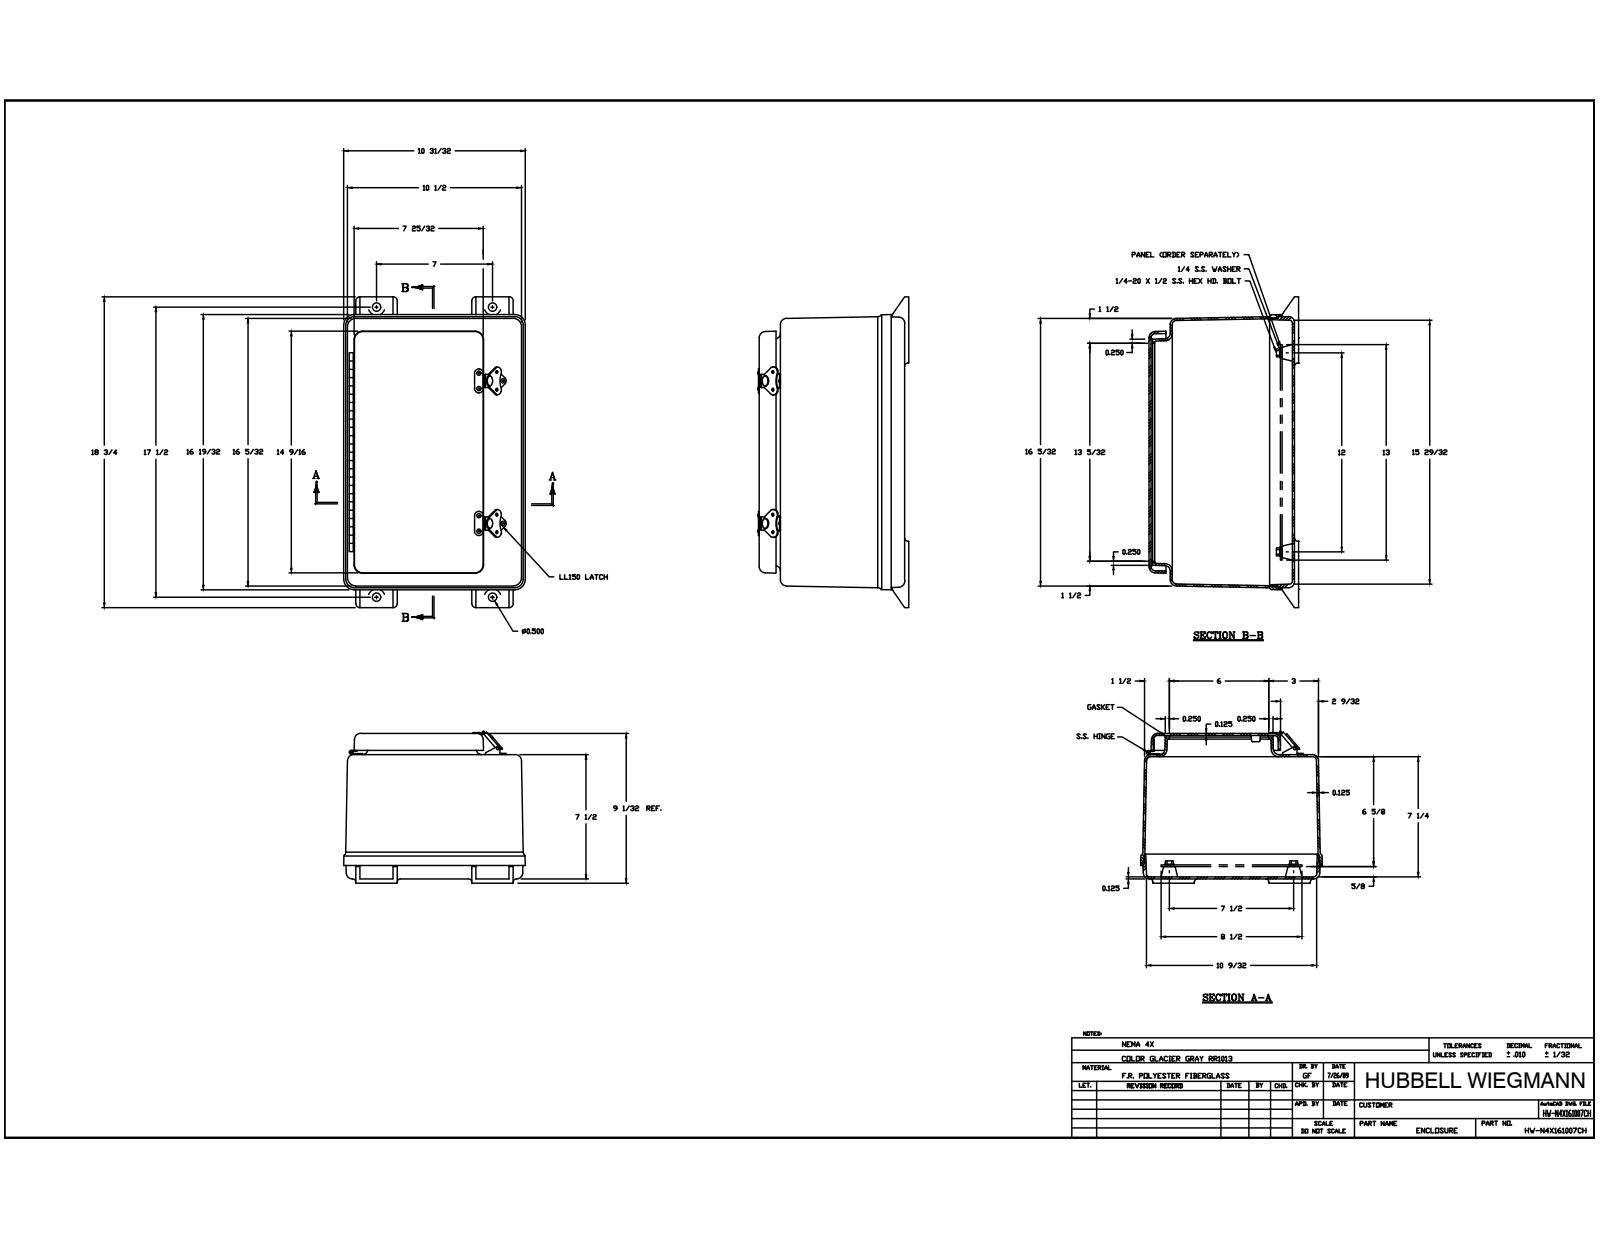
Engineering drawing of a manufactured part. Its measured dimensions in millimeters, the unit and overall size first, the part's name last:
Units: millimetres
Overall size (bounding box): 476.25 × 278.61 × 233.82
Round holes (diameter × count): ⌀3.3 ×17, ⌀1.59 ×8, ⌀1.65 ×6, ⌀3.5 ×4, ⌀4.76 ×4, ⌀10.16 ×4, ⌀7.14 ×2, ⌀12.95 ×2, ⌀12.96 ×2, ⌀3.17 ×1, ⌀3.43 ×1, ⌀3.97 ×1
Round bosses / shafts (diameter × count): ⌀3.56 ×8, ⌀7.54 ×6, ⌀12.7 ×2, ⌀6.35 ×1, ⌀5.08 ×1
Partial cylindrical surfaces — rounded edges, fillets, slot ends (radius × count): R0.25 ×59, R6.35 ×28, R9.53 ×22, R4.76 ×14, R12.7 ×12, R7.94 ×10, R0.76 ×8, R2.54 ×5
Main face-to-face distances: 3.17, 3.18, 219.87, 187.32, 223.04, 219.86, 216.69, 32.55, 190.49, 29.37
Hole centre spacings: 139.7, 23.81, 219.07, 233.86, 219.1, 38.41, 38.42, 210.37
Volume: 2 051 000 mm³ · Surface area: 1 223 000 mm²
Bodies: 31 solids, 1013 faces (385 planar, 378 cylindrical, 250 other)
Part name (STEP PRODUCT): WPN16107SHWT; WPN1610B; WPN16107HWTPCVR; N16107G (+8 more)
STEP written by: Autodesk Inventor 2014 (AUTOMOTIVE_DESIGN)
